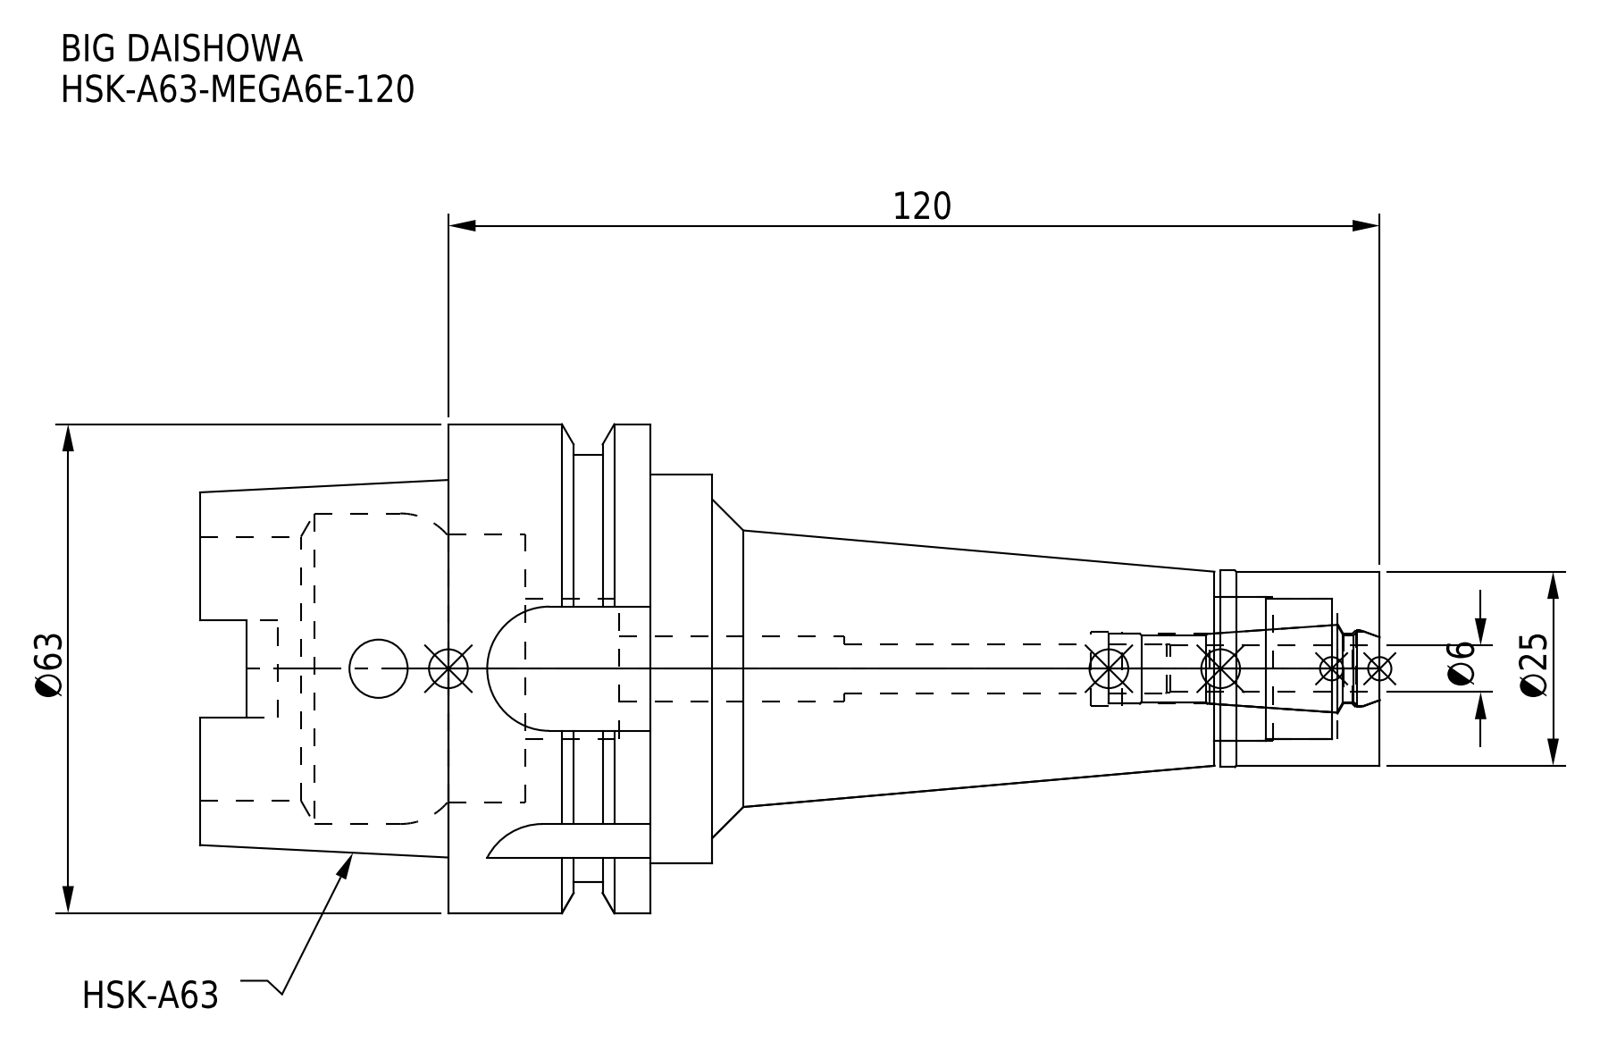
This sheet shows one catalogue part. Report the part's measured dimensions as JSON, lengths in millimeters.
{"part_name": "HSK-A63-MEGA6E-120-060-FreeParts; HSK-A63-MEGA6E-120; MEN6_1.stp; HA63ME06120-060_ASM.stp (+3 more)", "step_written_by": "SolidWorks 2019 (CONFIG_CONTROL_DESIGN)", "units": "millimeters", "bodies": {"solids": 2, "faces": 127, "planar": 45, "cylindrical": 54, "other": 28}, "overall_size": [152, 63, 63], "volume_mm3": 151612, "surface_area_mm2": 35713, "round_holes": [[6.4, 1], [7.5, 1], [8.4, 1], [9, 1], [9.6, 1], [9.9, 1], [18, 1], [18.5, 1], [34, 1], [34.5, 1], [40, 1]], "round_bosses_or_shafts": [[63, 1], [55, 1], [50, 1], [25.3, 1], [25, 1]], "partial_cylinders_radius": [[2.8, 2], [2.88, 2], [8, 2], [9, 1]], "face_to_face_distances": [26, 16.05, 9.95, 8, 24.05, 34, 86, 94, 110.05, 120]}
